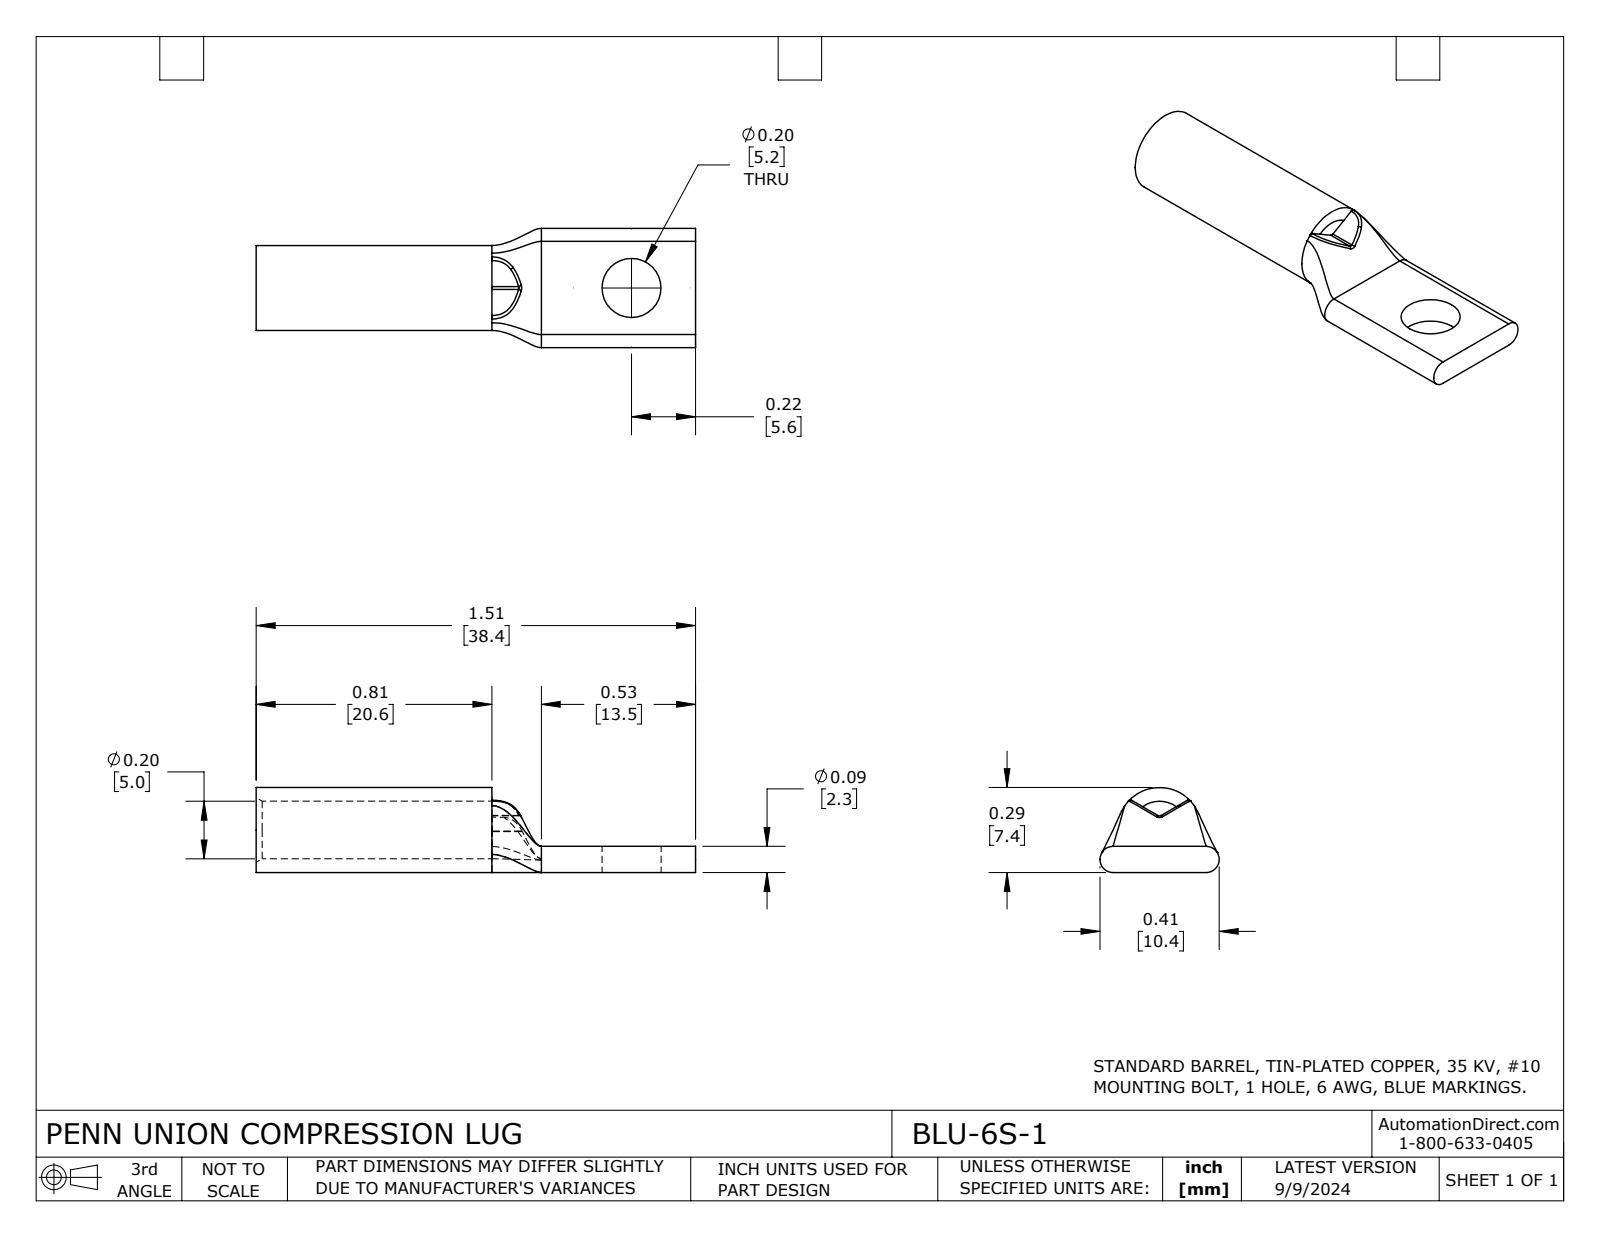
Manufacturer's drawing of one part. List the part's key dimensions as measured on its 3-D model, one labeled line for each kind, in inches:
Part name (STEP PRODUCT): BLU-6S-1
STEP written by: SolidWorks 2023 (CONFIG_CONTROL_DESIGN)
Units: inches
Bodies: 1 solid, 38 faces (11 planar, 11 cylindrical, 16 other)
Overall size (bounding box): 1.51 × 0.41 × 0.292
Volume: 0.051 in³ · Surface area: 2.118 in²
Round holes (diameter × count): ⌀0.198 ×1, ⌀0.203 ×1
Round bosses / shafts (diameter × count): ⌀0.292 ×1
Partial cylindrical surfaces — rounded edges, fillets, slot ends (radius × count): R0.01 ×2, R0.045 ×2
Main face-to-face distances: 0.09, 1.51, 0.81, 0.7, 0.047, 0.98, 0.17, 0.53
